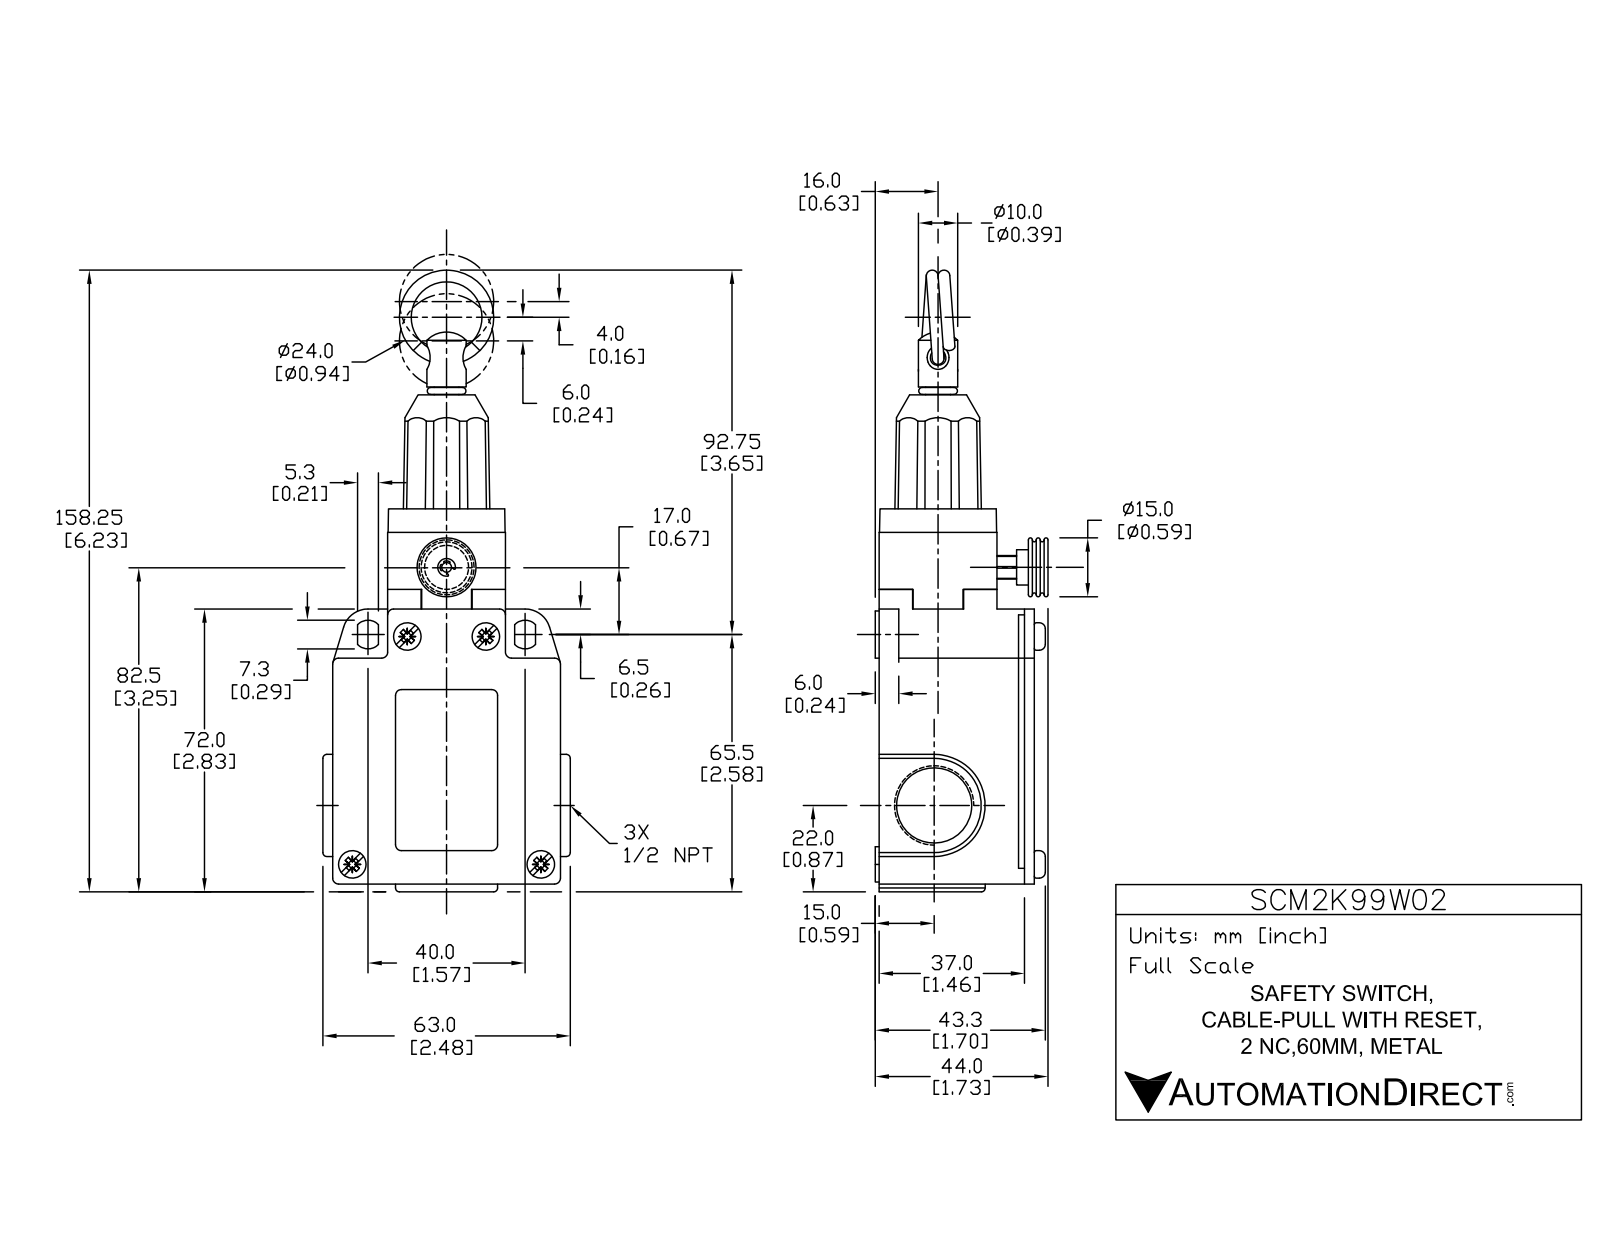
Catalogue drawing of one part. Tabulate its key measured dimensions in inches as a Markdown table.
| quantity | value |
| --- | --- |
| part name | SCM2K99W02 |
| STEP written by | SolidWorks 2017 (AUTOMOTIVE_DESIGN) |
| units | inches |
| bodies | 5 solids, 256 faces (100 planar, 94 cylindrical, 62 other) |
| overall size | 6.28 × 2.441 × 1.724 |
| volume | 11.03 in³ |
| surface area | 50.03 in² |
| round holes (diameter × count) | 0.669 × 2, 0.748 × 2, 0.157 × 1, 0.398 × 1, 0.709 × 1 |
| round bosses / shafts (diameter × count) | 0.276 × 4, 0.472 × 2, 0.354 × 2, 0.701 × 1, 0.394 × 1, 0.386 × 1, 0.264 × 1, 0.248 × 1 |
| partial cylindrical surfaces (radius × count) | 0.059 × 12, 0.144 × 2, 0.256 × 2, 0.512 × 2, 0.453 × 1, 0.472 × 1 |
| main face-to-face distances | 1.555, 0.551, 1.732, 1.181, 2.283, 0.079, 0.236, 0.157, 0.197, 2.756 |
| hole center spacings | 0.039, 4.528 |
